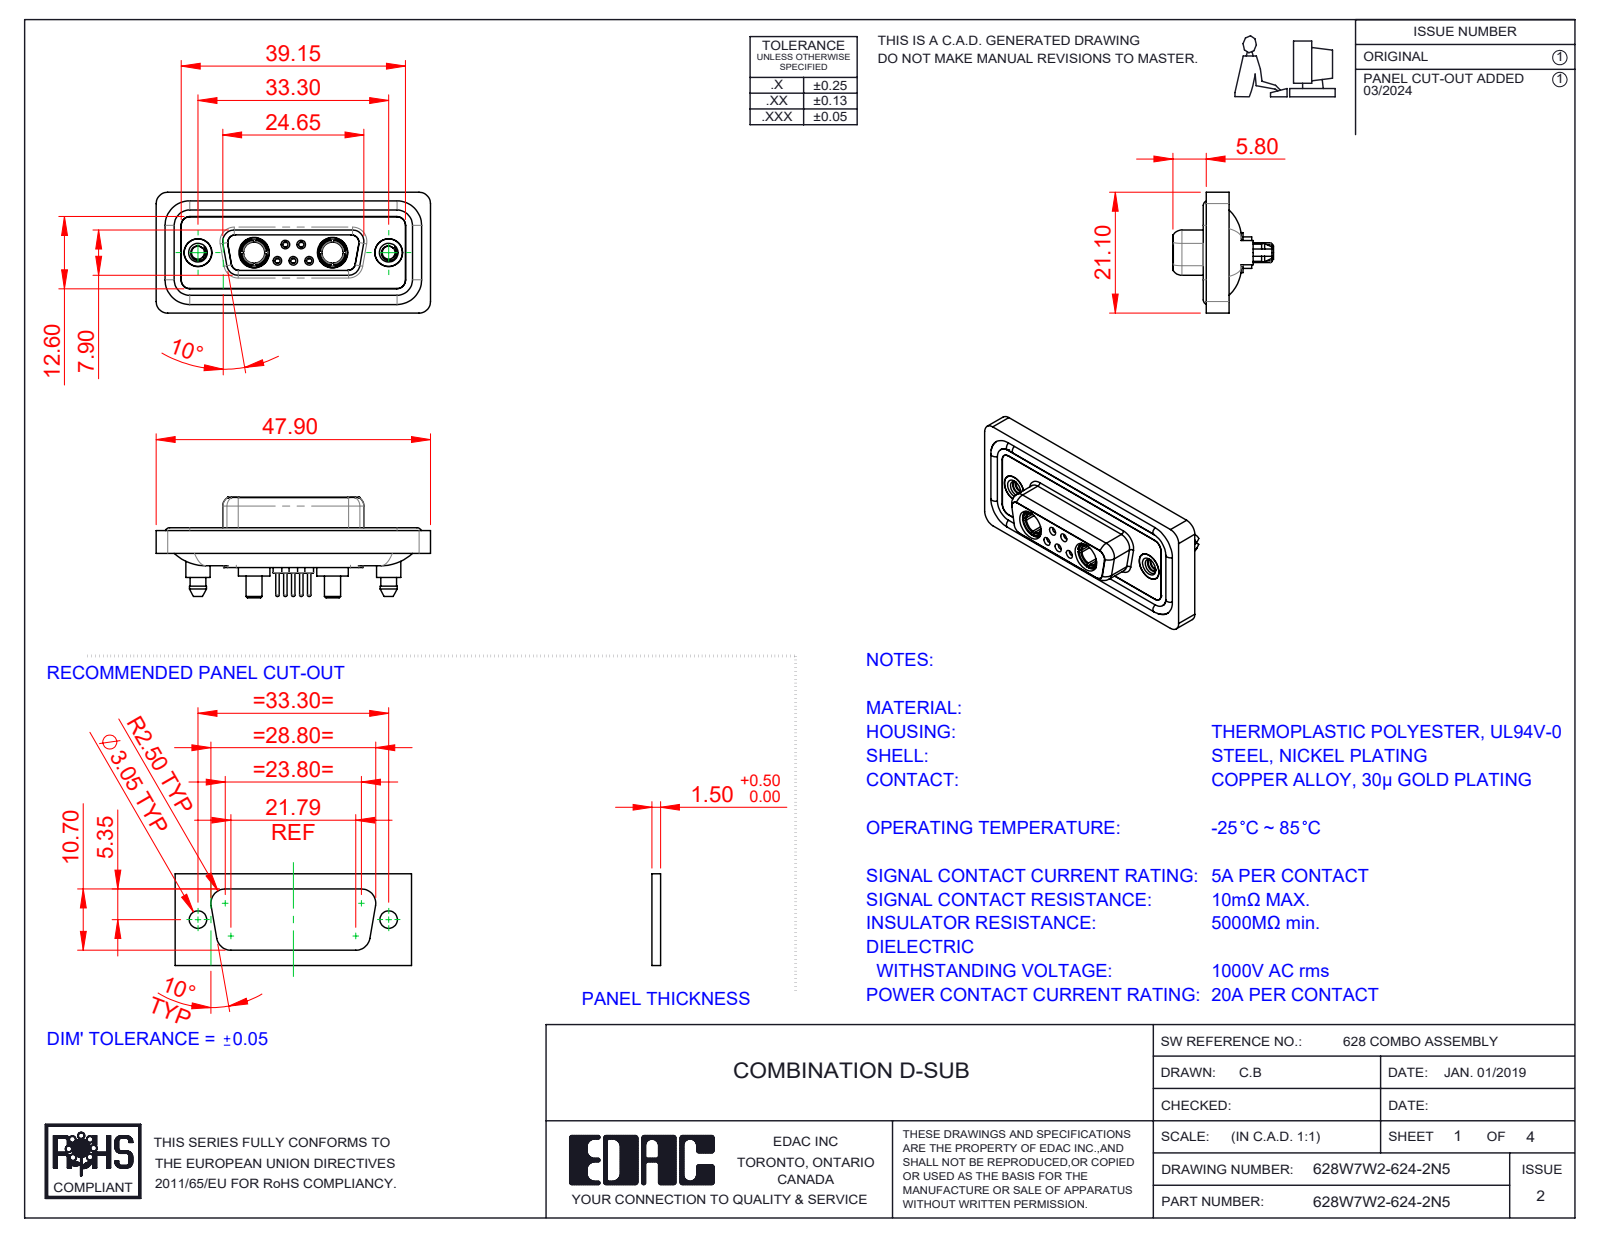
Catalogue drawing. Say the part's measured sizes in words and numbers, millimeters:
The part is named "628Combo Contact Row 2_24; 628Combo Contact Row 1_24; 628Combo Threaded Boardlock_5; 628Combo Shell Front_15 Contacts (+5 more)". Its 3-D file was written by "SolidWorks 2023 (CONFIG_CONTROL_DESIGN)". It is 16 solids with 859 faces: 254 planar, 361 cylindrical and 244 other. Overall it measures 47.9 by 21.1 by 17.55 millimeters. Its volume is 6 211 cubic millimeters and its surface area 10 218 square millimeters. Round holes: 5 of diameter 0.9, 5 of diameter 1.1, 5 of diameter 1.5, 5 of diameter 2, 4 of diameter 4.85, 3 of diameter 1.6, 2 of diameter 1.7, 2 of diameter 2.26, 2 of diameter 3.7, 2 of diameter 4, 2 of diameter 4.05, 2 of diameter 5. Round bosses or shafts: 6 of diameter 1.6, 5 of diameter 2.2, 5 of diameter 0.6, 2 of diameter 5.5, 2 of diameter 5.4, 2 of diameter 5.2, 2 of diameter 4.96, 2 of diameter 4.95. Partial cylindrical surfaces (rounded edges, fillets, slot ends): 24 of radius 1.5, 20 of radius 2, 12 of radius 1.35, 10 of radius 1.6, 4 of radius 0.25, 4 of radius 0.5, 4 of radius 0.6, 4 of radius 0.65. The main face-to-face distances are 0.4, 1.8, 1.6, 0.5, 2.9, 1.1, 7.45, 5.65, 6.6, 7.05. The hole center spacings are 3.16, 2.77, 9.8, 23.5, 4.31, 4.33, 5.03, 5.04.
